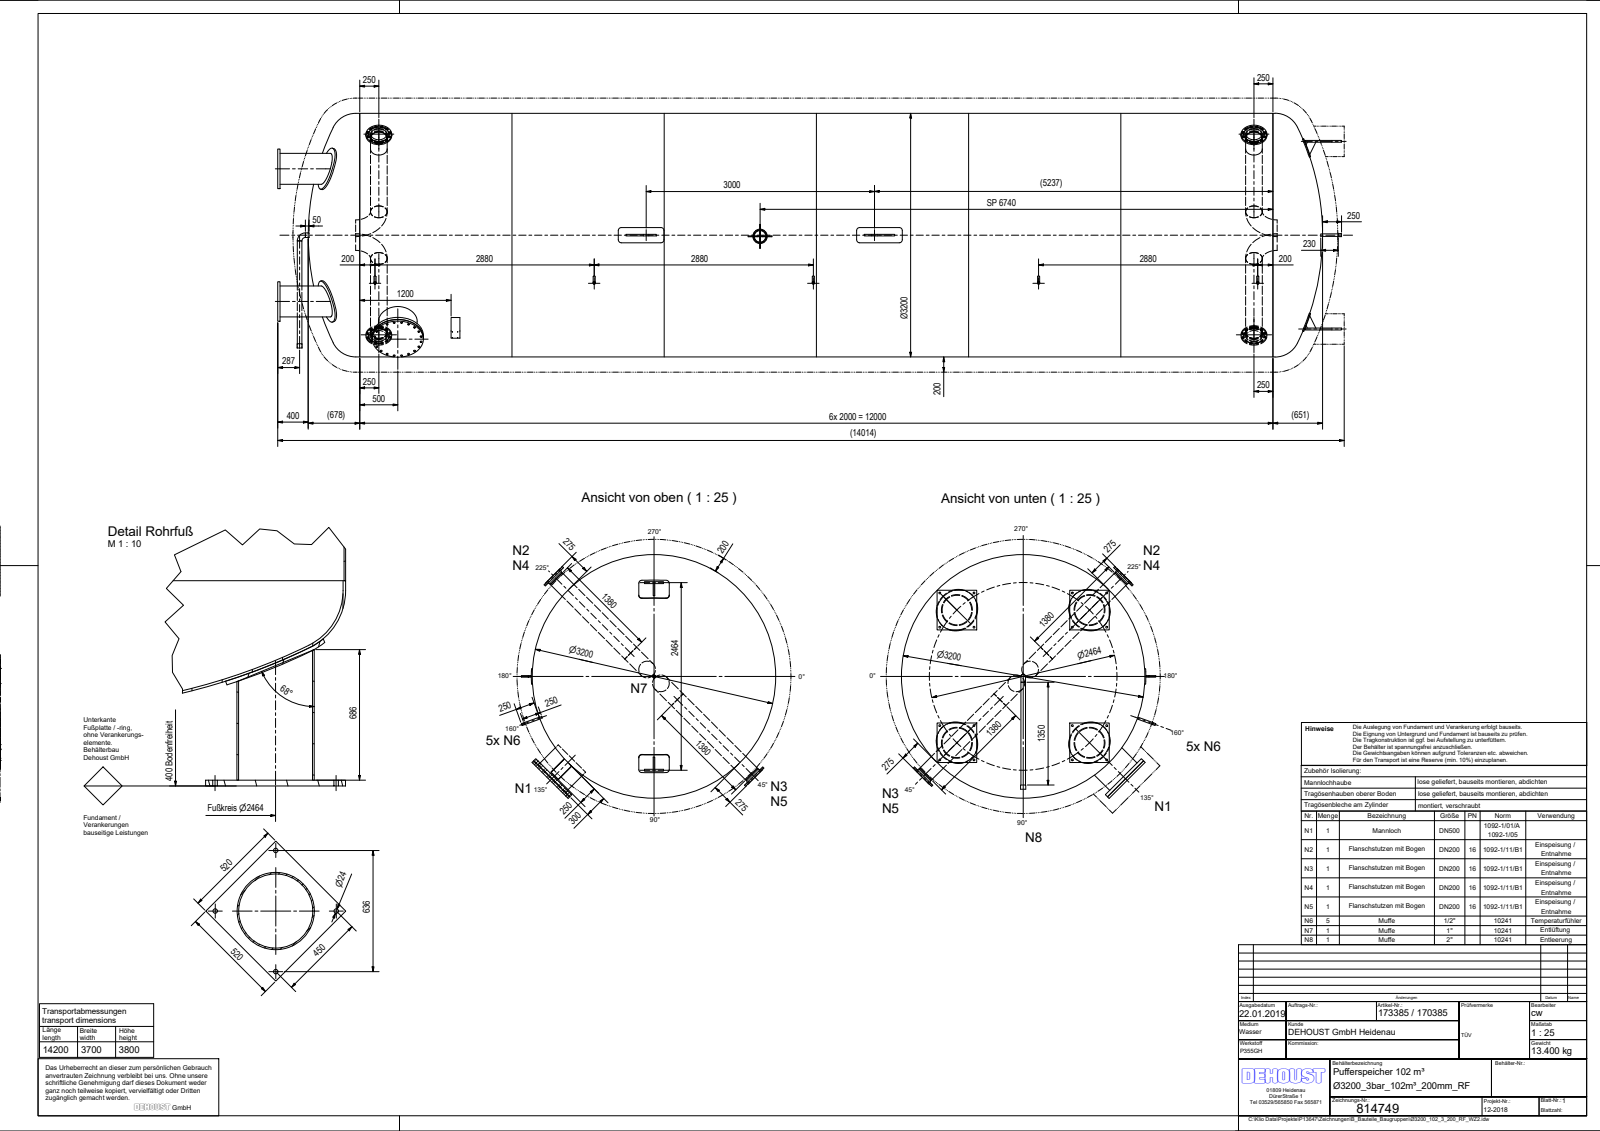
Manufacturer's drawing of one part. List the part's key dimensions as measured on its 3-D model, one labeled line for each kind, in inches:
Part name (STEP PRODUCT): Ø3200_102_3_200_RF_WZ2; Klöpper_Gew_Ø3200_7,1; Klöpper_Gew_Ø3200_13,0; Zyl_Ø3200_8x12000_2019 (+8 more)
STEP written by: Autodesk Inventor 2019 (AUTOMOTIVE_DESIGN)
Units: inches
Bodies: 58 solids, 457 faces (176 planar, 231 cylindrical, 50 other)
Overall size (bounding box): 550.378 × 131.612 × 126.075
Volume: 98 980 in³ · Surface area: 483 100 in²
Round holes (diameter × count): ⌀0.866 ×48, ⌀1.024 ×40, ⌀0.945 ×16, ⌀0.733 ×5, ⌀0.854 ×5, ⌀1.059 ×5, ⌀0.228 ×4, ⌀8.13 ×4, ⌀8.161 ×4, ⌀8.626 ×4, ⌀15.307 ×4, ⌀2.059 ×2
Round bosses / shafts (diameter × count): ⌀8.626 ×8, ⌀1.059 ×5, ⌀1.039 ×5, ⌀22.047 ×4, ⌀16 ×4, ⌀13.386 ×4, ⌀10.551 ×4, ⌀26.378 ×2
Partial cylindrical surfaces — rounded edges, fillets, slot ends (radius × count): R1.575 ×8, R1.654 ×8, R0.197 ×2, R0.394 ×2, R2.835 ×2, R4.921 ×1, R63.465 ×1
Main face-to-face distances: 1.181, 23.622, 219.783, 252.657, 262.235, 295.109, 261.054, 293.928, 32.874, 1.102
Hole centre spacings: 5.807, 12.205, 7.543, 19.748, 5.807, 113.386, 14.348, 23.215
